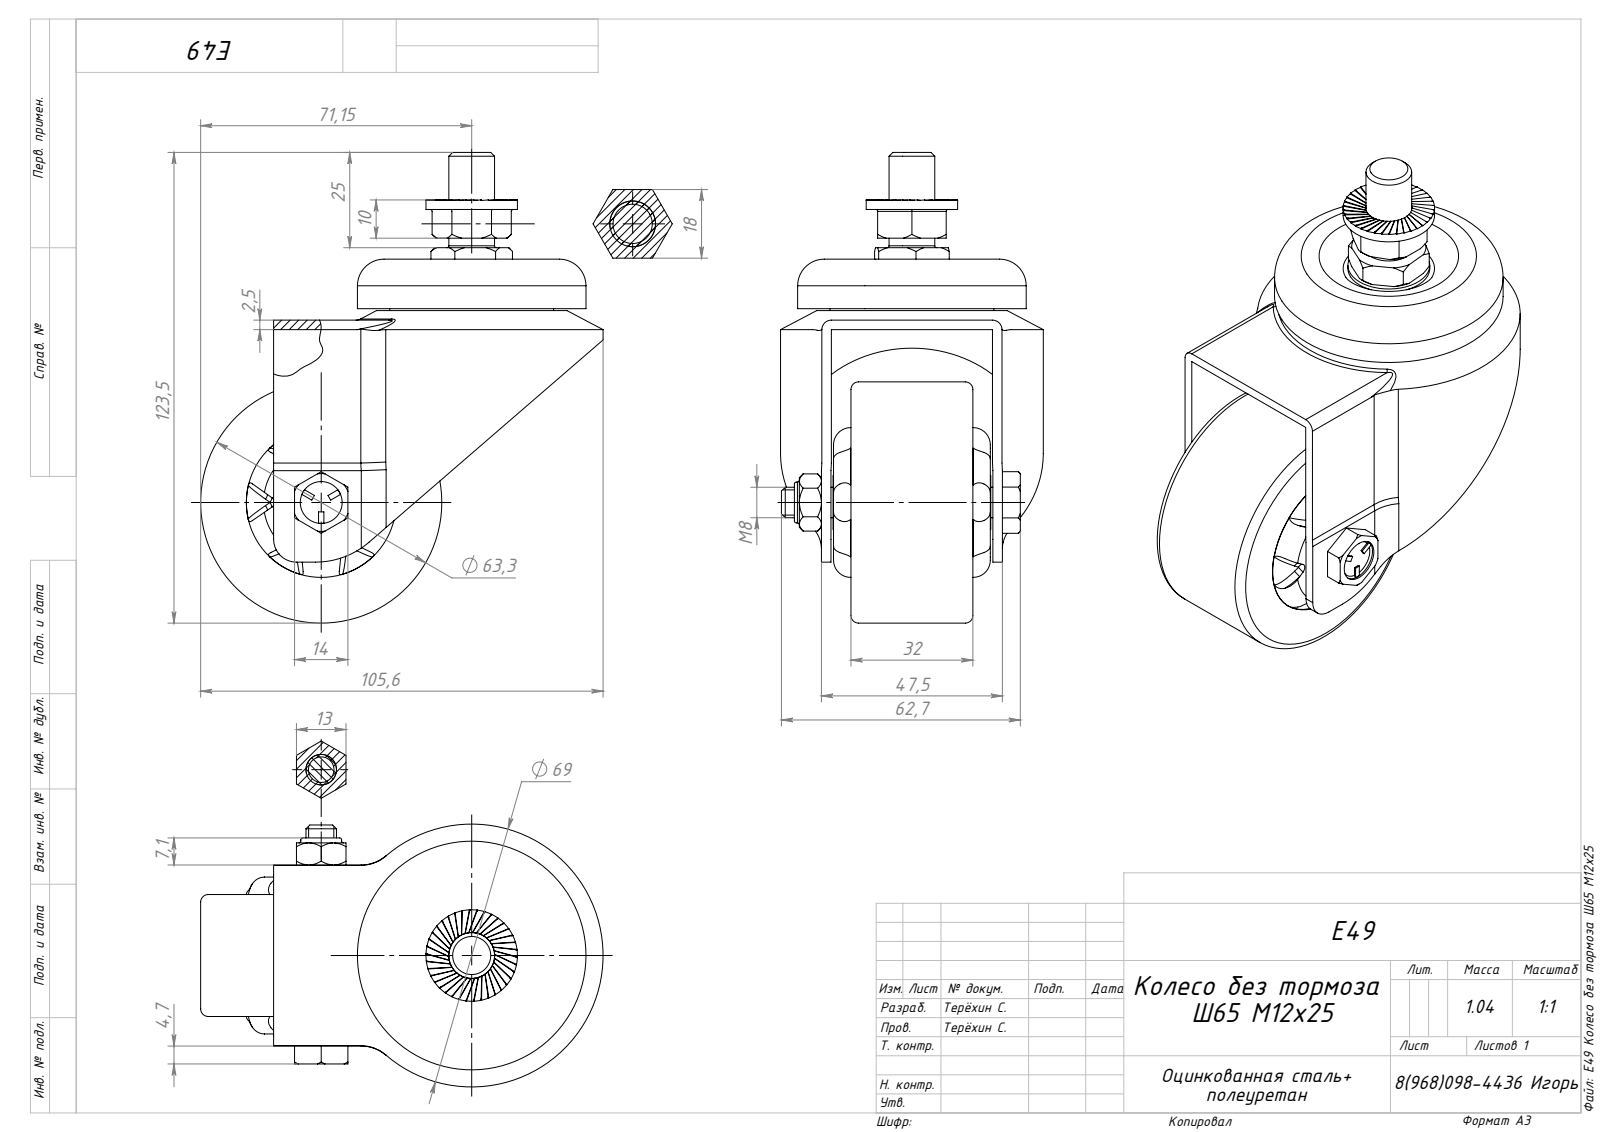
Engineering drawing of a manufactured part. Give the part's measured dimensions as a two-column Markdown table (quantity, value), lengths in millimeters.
| quantity | value |
| --- | --- |
| part name | SNSD.30.50.70. Болт(E49)_00; SNSD.30.50.70. Подшипниковый узел(E49)E45_00; SNSD.30.50.70. Втулка(E49)_00; SNSD.30.50.70. Опора(E49)E45_й (+4 more) |
| STEP written by | SolidWorks 2026 (AUTOMOTIVE_DESIGN) |
| units | millimeters |
| bodies | 7 solids, 443 faces (225 planar, 61 cylindrical, 157 other) |
| overall size | 123.5 × 105.64 × 68.97 |
| volume | 186 272 mm³ |
| surface area | 58 370 mm² |
| round holes (diameter × count) | 6.7 × 1, 8.2 × 1, 10.3 × 1, 11 × 1, 39.3 × 1, 43 × 1 |
| round bosses / shafts (diameter × count) | 63.3 × 1, 60 × 1, 45 × 1, 24 × 1, 21.5 × 1, 14 × 1, 12 × 1, 10.7 × 1 |
| partial cylindrical surfaces (radius × count) | 0.5 × 7, 10 × 4, 2.5 × 2, 6 × 1, 21.5 × 1, 31.99 × 1, 34.49 × 1 |
| main face-to-face distances | 2.5, 0.5, 44.9, 5.15, 37.15, 5, 32, 7.65, 39.65, 44.8 |
